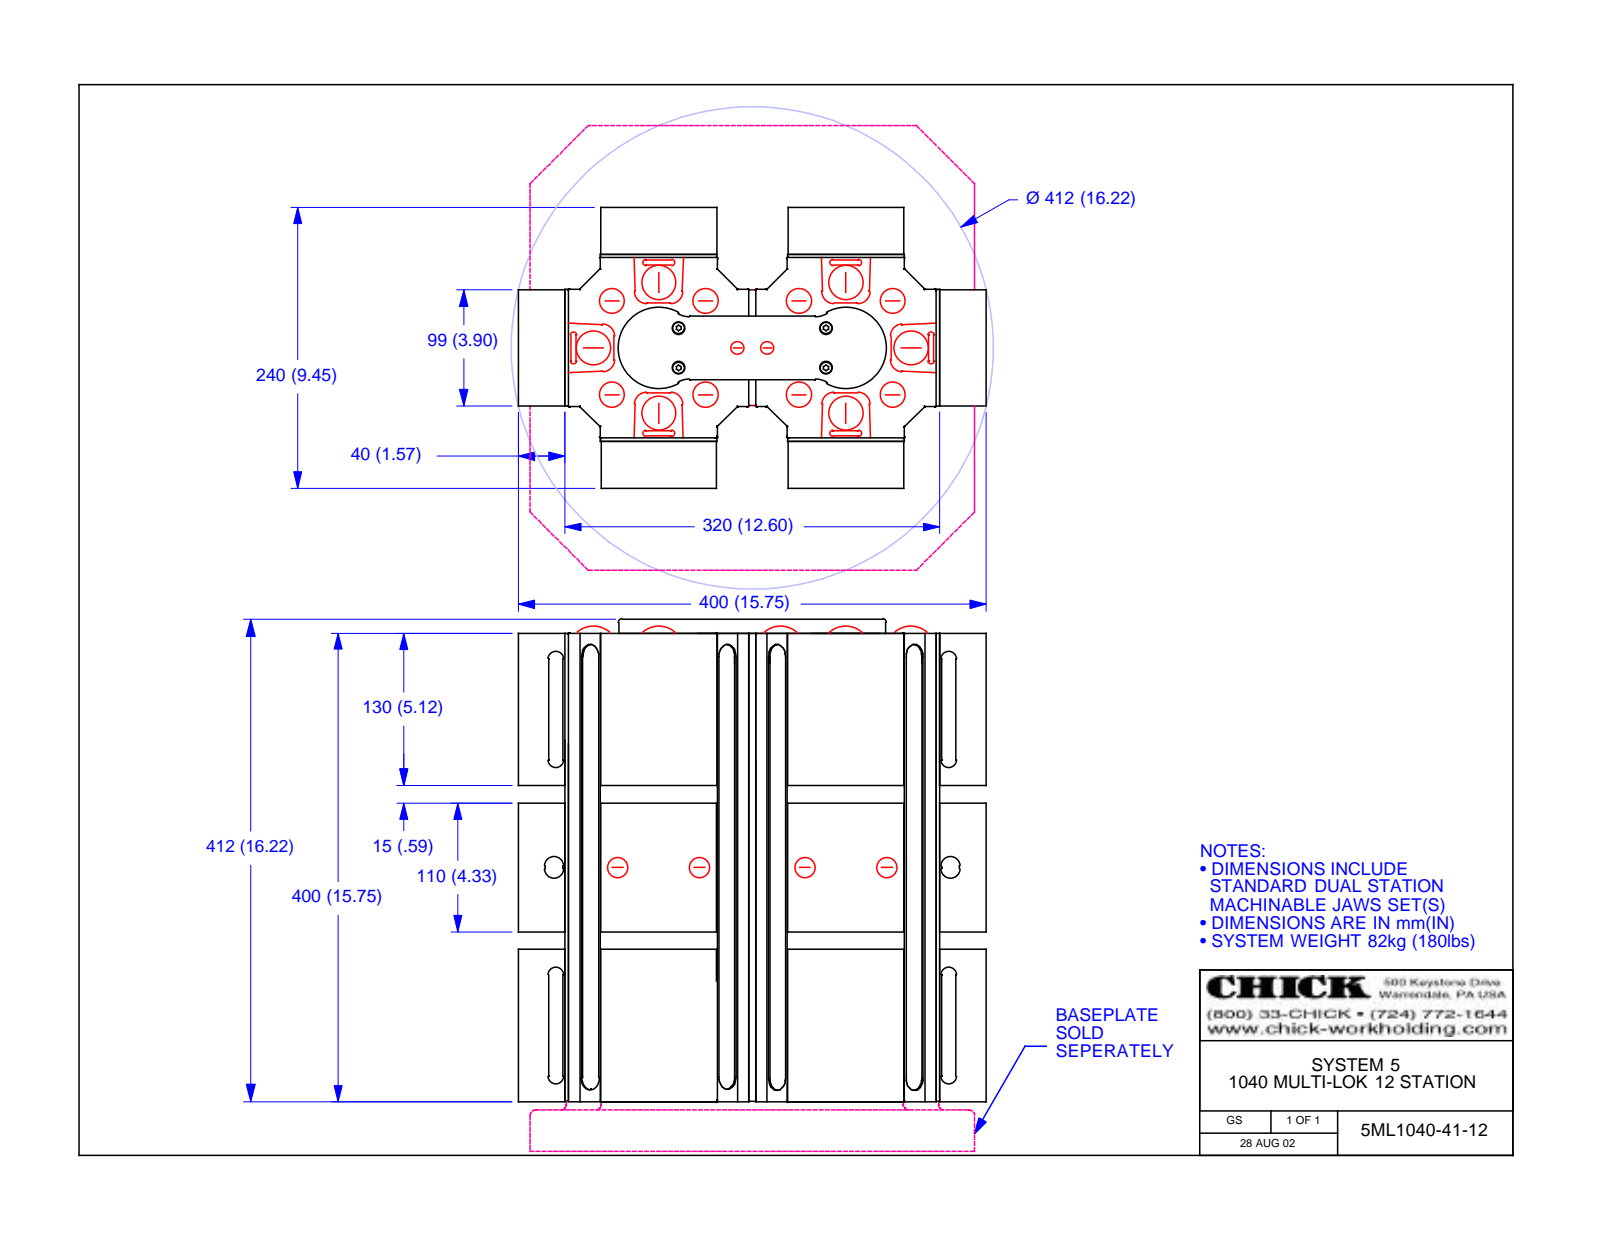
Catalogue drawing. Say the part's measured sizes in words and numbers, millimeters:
The part is named "5ML1040-41-12; 5CLM1040-41-12; 5DS1040-10-40; 5FJ1040-10-40 (+2 more)". Its 3-D file was written by "Autodesk Inventor 2013 (AUTOMOTIVE_DESIGN)". It is 25 solids with 4408 faces: 2354 planar, 784 cylindrical and 1270 other. Overall it measures 412 by 399.4 by 239.4 millimeters. Its volume is 23 920 000 cubic millimeters and its surface area 2 029 000 square millimeters. Round holes: 18 of diameter 6.65, 18 of diameter 9, 18 of diameter 14.15, 18 of diameter 19.34, 16 of diameter 10.11, 12 of diameter 8.65, 12 of diameter 10, 12 of diameter 12.7, 8 of diameter 4.06, 8 of diameter 4.92, 8 of diameter 6.87, 8 of diameter 20. Round bosses or shafts: 10 of diameter 8.4, 8 of diameter 7.67, 8 of diameter 4.76. Partial cylindrical surfaces (rounded edges, fillets, slot ends): 108 of radius 1.5, 32 of radius 0.4, 32 of radius 1.2, 24 of radius 4.8, 24 of radius 11.1, 16 of radius 1.65, 16 of radius 2.83, 16 of radius 7. The main face-to-face distances are 3, 157, 160, 39.7, 42.7, 196.7, 154, 64.99, 89.01, 199.7. The hole center spacings are 113.14, 70, 160, 1.22, 58.6, 67.19, 73.82, 83.87.
